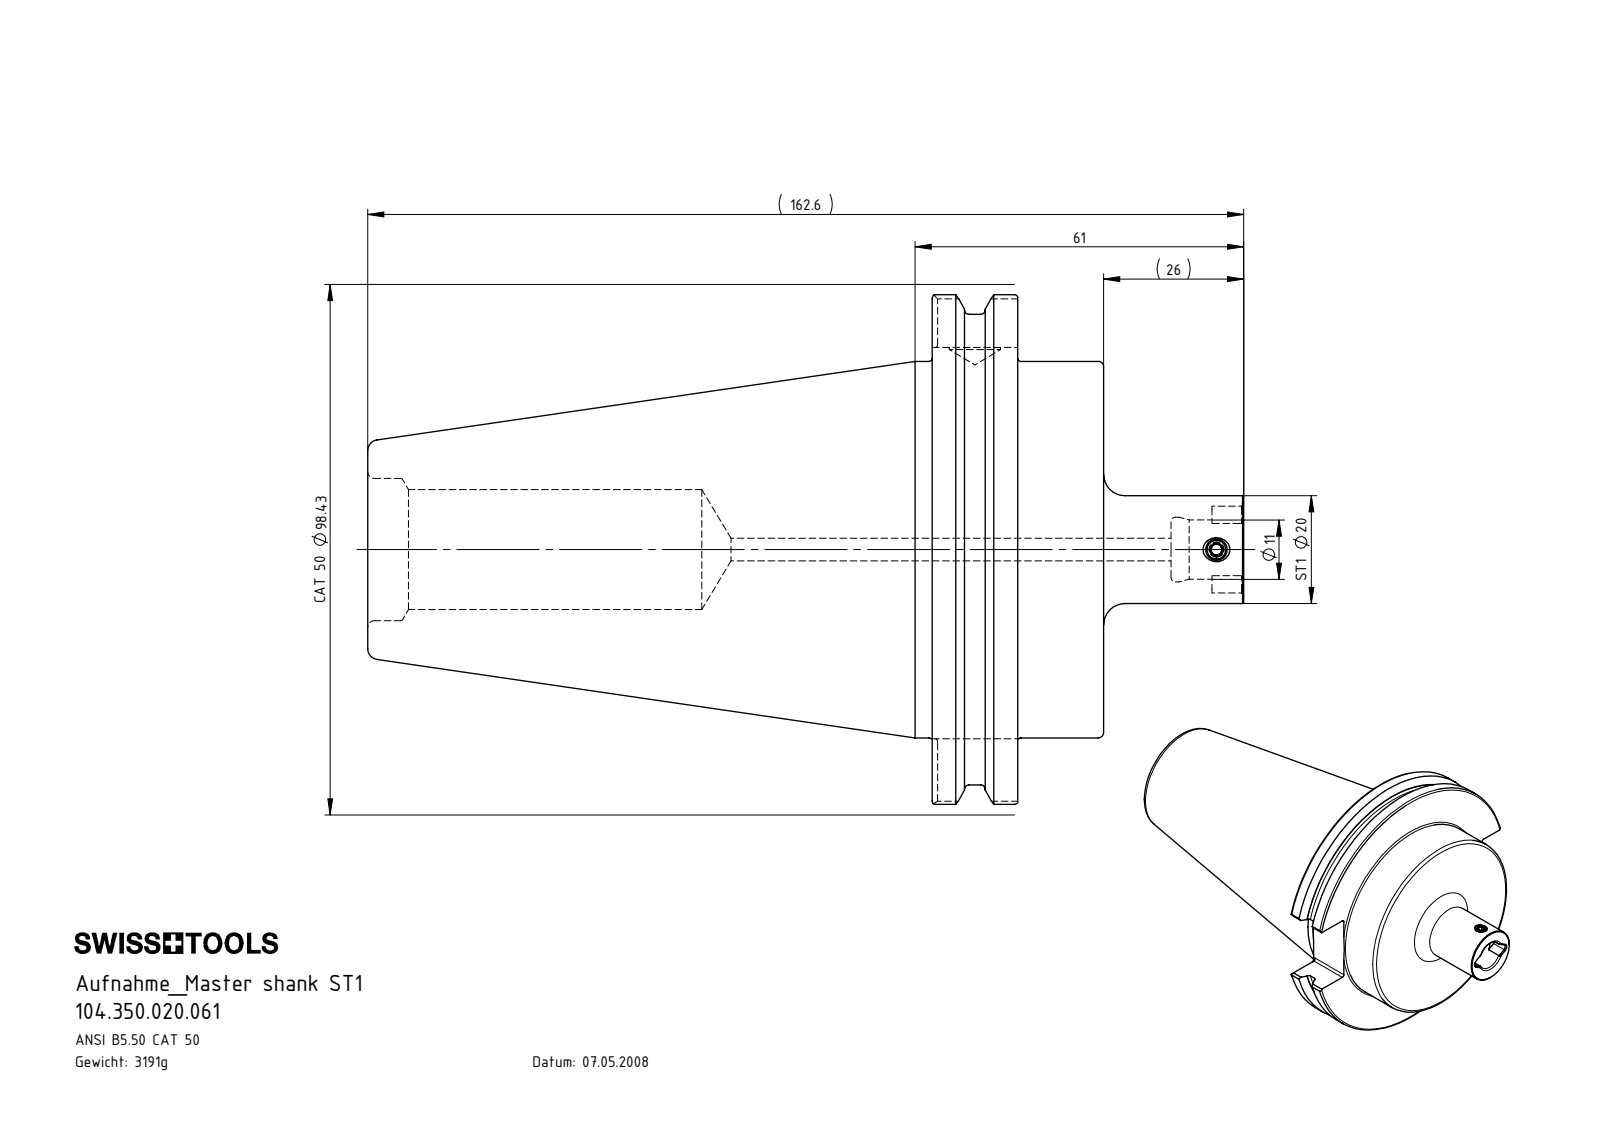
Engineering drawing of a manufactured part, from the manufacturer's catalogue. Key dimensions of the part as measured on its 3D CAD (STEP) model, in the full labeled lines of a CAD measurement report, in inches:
Part name (STEP PRODUCT): ST1-ER1.001.005_A; CT5-ST1.K01.061_B; CT5.ST1.K01.061
STEP written by: SolidWorks 2017 (AUTOMOTIVE_DESIGN)
Units: inches
Bodies: 2 solids, 115 faces (50 planar, 28 cylindrical, 37 other)
Overall size (bounding box): 6.402 × 3.875 × 3.721
Volume: 24.8 in³ · Surface area: 72.76 in²
Round holes (diameter × count): ⌀0.079 ×1, ⌀0.138 ×1, ⌀0.165 ×1, ⌀0.374 ×1, ⌀0.433 ×1, ⌀0.472 ×1, ⌀0.876 ×1, ⌀1.039 ×1
Round bosses / shafts (diameter × count): ⌀3.875 ×1, ⌀3.583 ×1, ⌀2.75 ×1, ⌀0.787 ×1, ⌀0.157 ×1
Partial cylindrical surfaces — rounded edges, fillets, slot ends (radius × count): R0.031 ×8, R0.051 ×2
Main face-to-face distances: 0.628, 0.625, 1.253, 4.125, 4.75, 5.378, 2.858, 1.012, 6.402, 2.276
